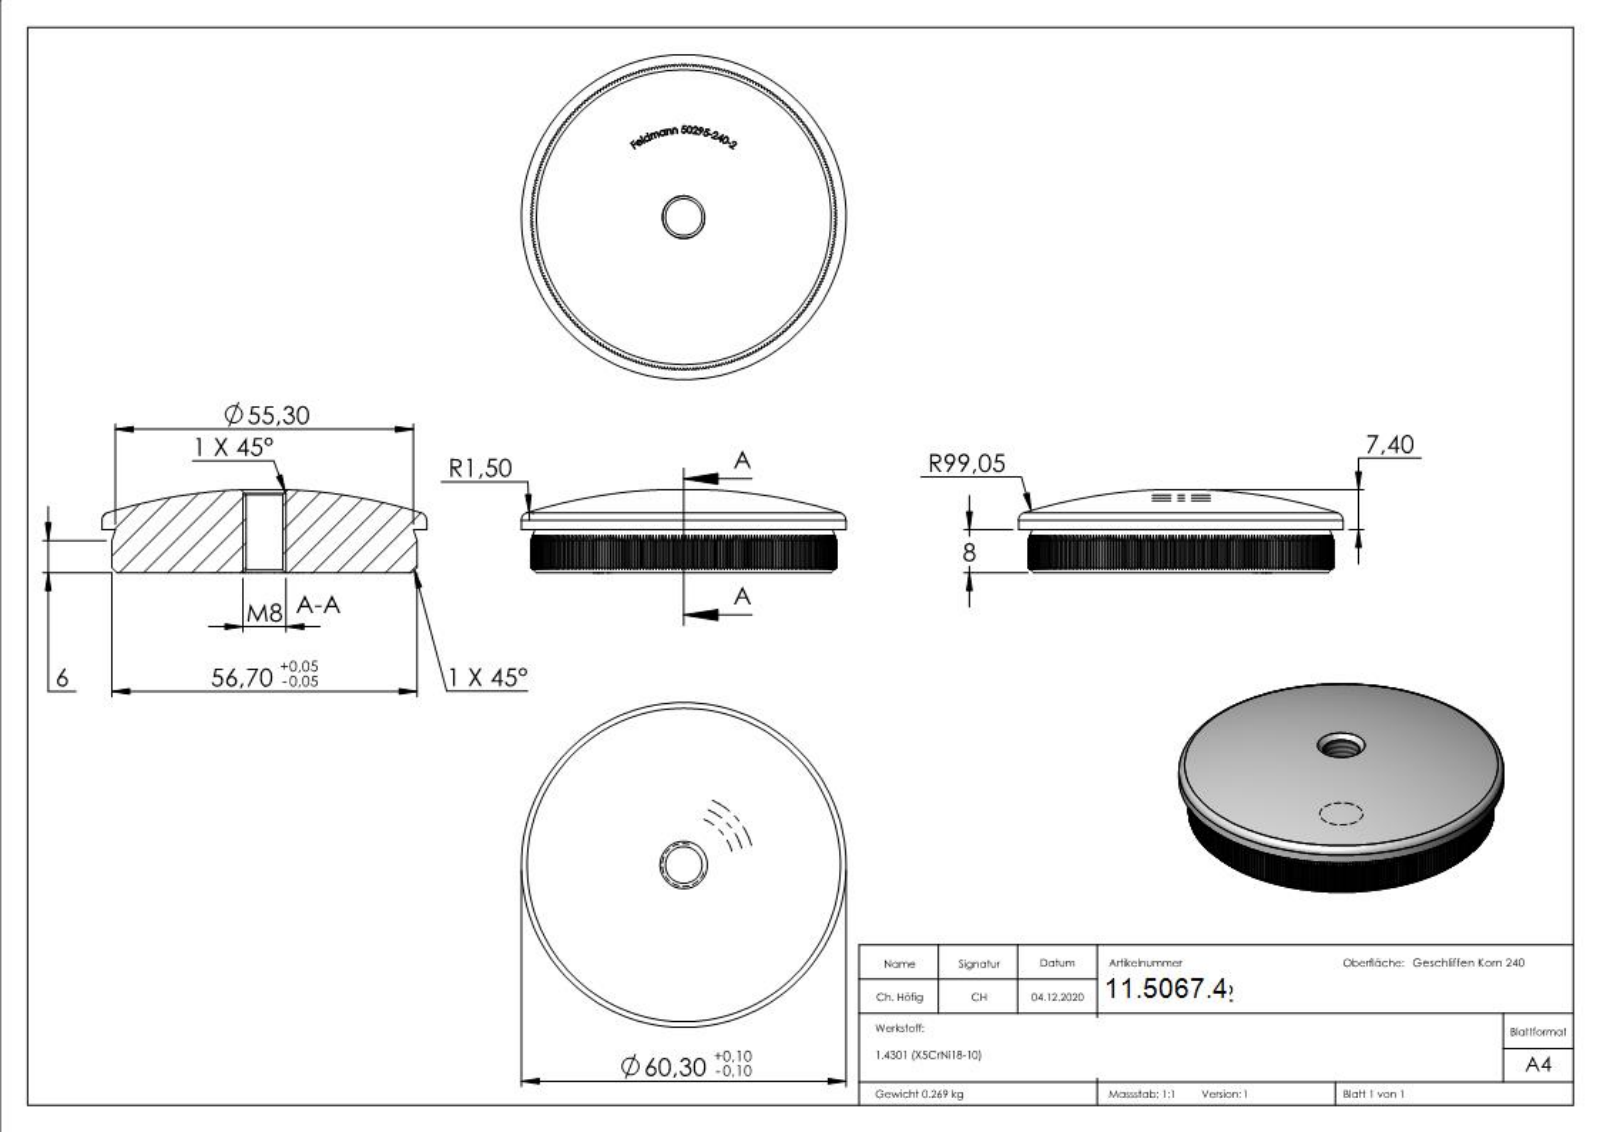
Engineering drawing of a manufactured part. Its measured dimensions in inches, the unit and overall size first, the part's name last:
Units: inches
Overall size (bounding box): 2.374 × 2.374 × 0.606
Round holes (diameter × count): ⌀0.268 ×1
Round bosses / shafts (diameter × count): ⌀2.374 ×1
Partial cylindrical surfaces — rounded edges, fillets, slot ends (radius × count): R1.116 ×1
Main face-to-face distances: 0.315, 1.102, 1.102, 1.103, 1.104, 1.101, 0.311, 0.021, 0.026, 0.57
Volume: 2.076 in³ · Surface area: 13.35 in²
Bodies: 1 solid, 1131 faces (716 planar, 294 cylindrical, 121 other)
Part name (STEP PRODUCT): 50295-240-2
STEP written by: SolidWorks 2015 (CONFIG_CONTROL_DESIGN)
